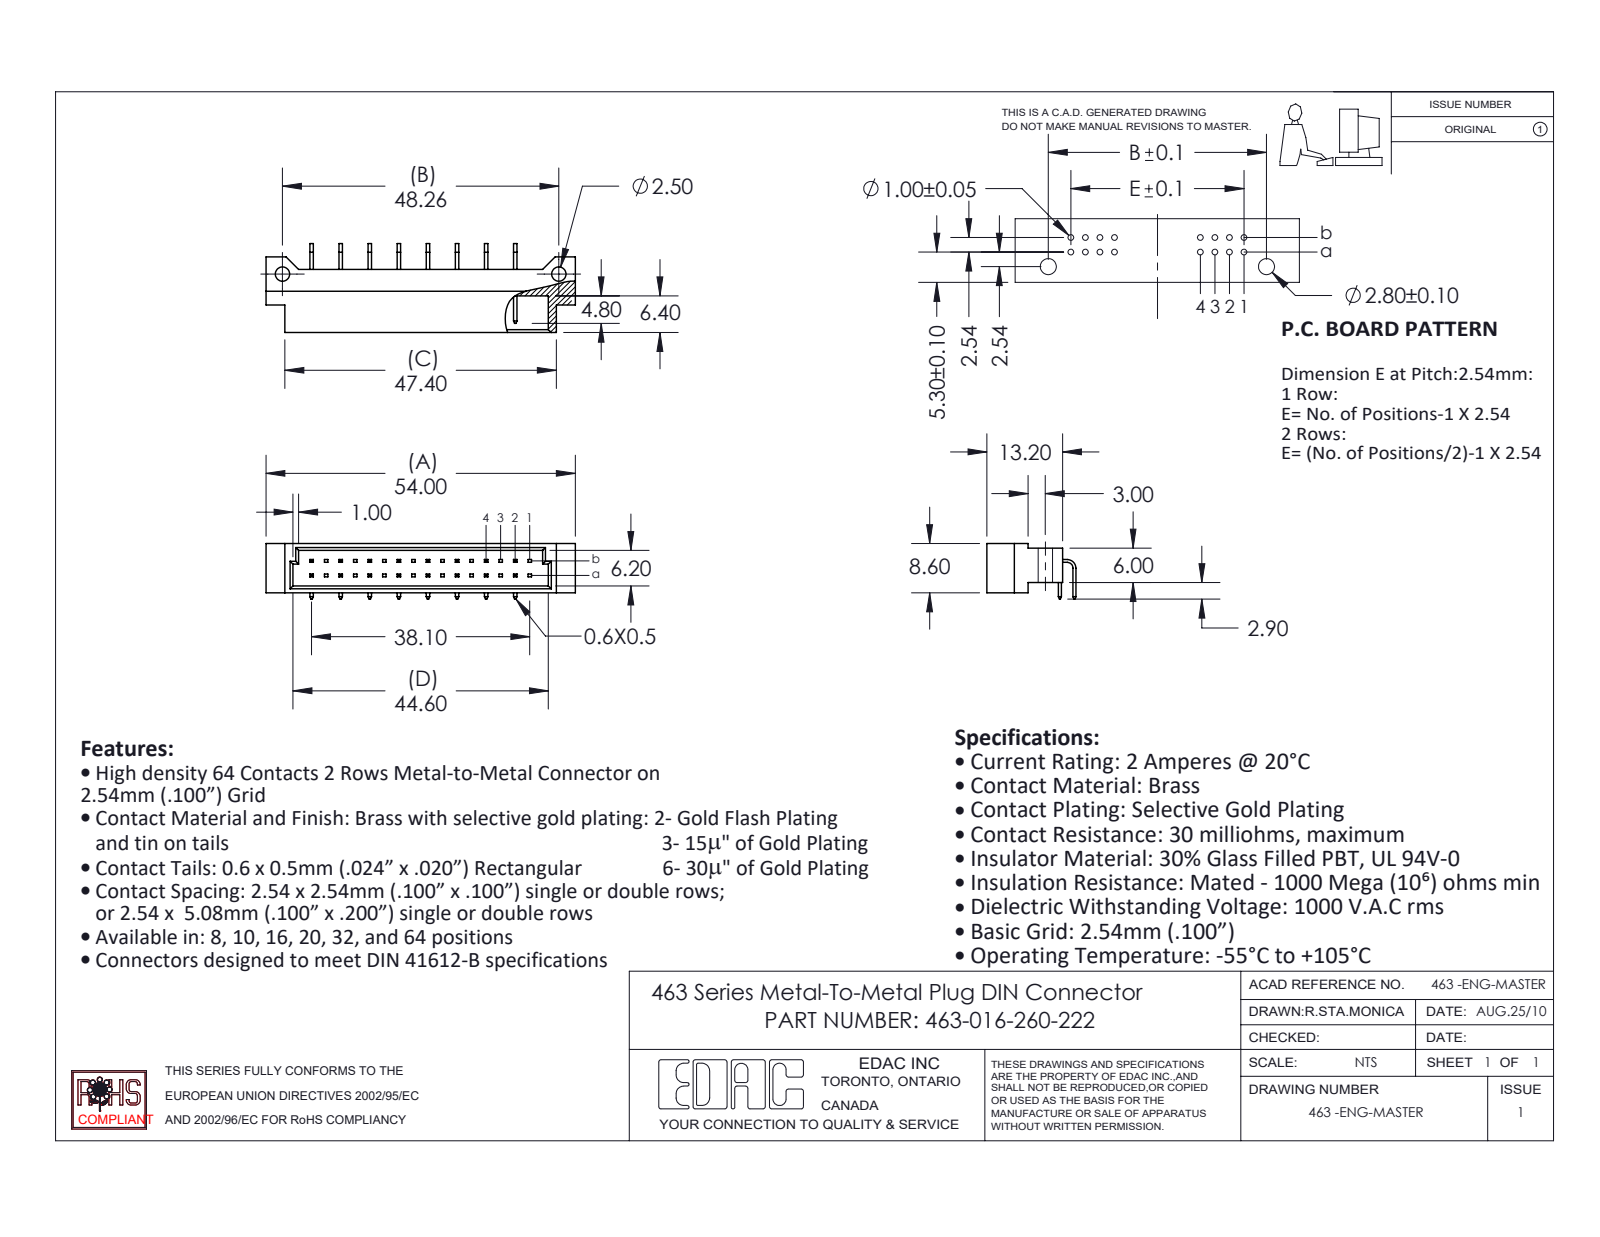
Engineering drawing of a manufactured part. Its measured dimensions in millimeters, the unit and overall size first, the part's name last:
Units: millimetres
Overall size (bounding box): 54 × 15.53 × 9.7
Round holes (diameter × count): ⌀2.5 ×2
Partial cylindrical surfaces — rounded edges, fillets, slot ends (radius × count): R1.02 ×2, R1.52 ×2
Main face-to-face distances: 1.2, 7.4, 0.6, 8.6, 0.8, 6.2, 6, 6.8, 5.08, 4.6
Hole centre spacings: 48.26
Volume: 2 650 mm³ · Surface area: 3 902 mm²
Bodies: 17 solids, 455 faces (419 planar, 36 cylindrical, 0 other)
Part name (STEP PRODUCT): 463-290-2; 463-290-1; 463 Part_32; 463-016-260-222
STEP written by: SolidWorks 2020 (CONFIG_CONTROL_DESIGN)
